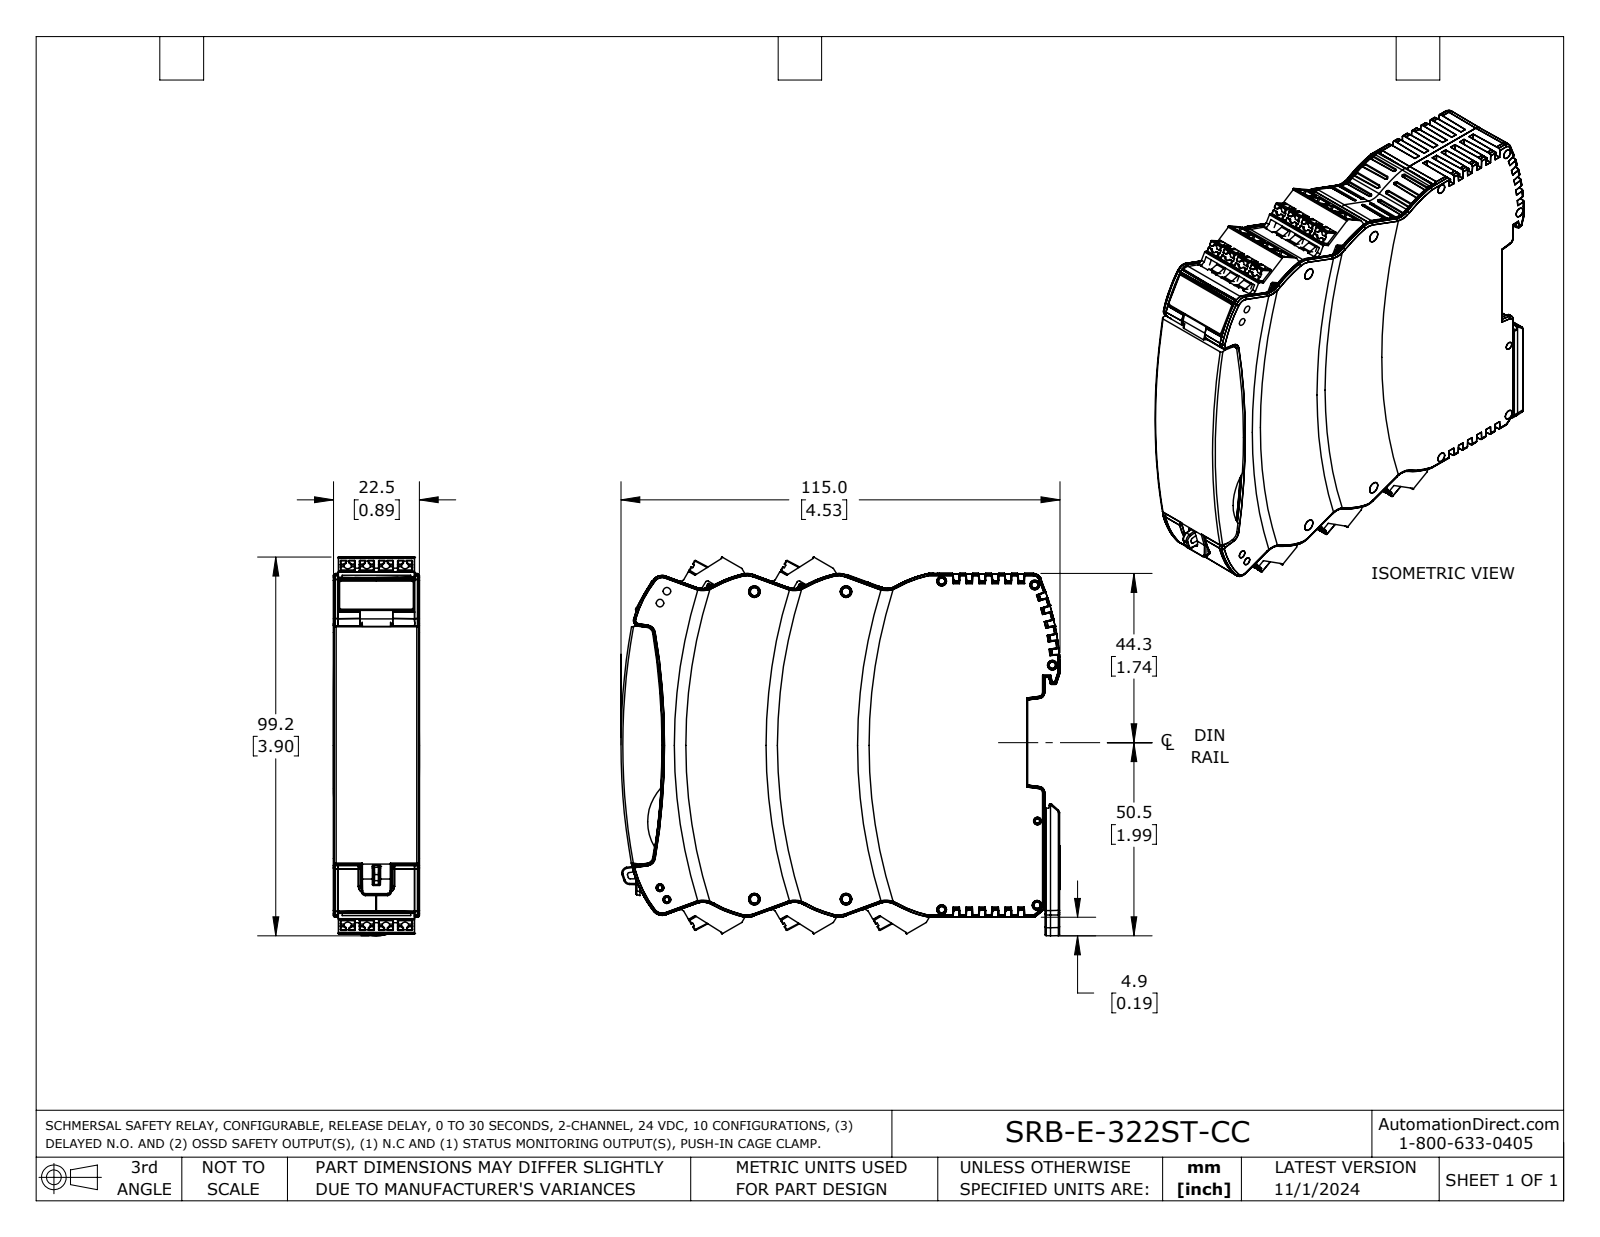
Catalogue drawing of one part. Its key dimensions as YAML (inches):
part_name: "SRB-E-322ST-CC"
step_written_by: "SolidWorks 2023 (AUTOMOTIVE_DESIGN)"
units: inches
bodies: {solids: 2, faces: 4715, planar: 2465, cylindrical: 1391, other: 859}
overall_size: [4.528, 3.904, 0.886]
volume: 12.97
surface_area: 68.52
round_bosses_or_shafts:
  - {diameter: 0.067, count: 1}
partial_cylinders:
  - {radius: 0.008, count: 260}
  - {radius: 0.012, count: 248}
  - {radius: 0.02, count: 206}
  - {radius: 0.01, count: 60}
  - {radius: 0.004, count: 55}
  - {radius: 0.039, count: 34}
  - {radius: 0.059, count: 24}
  - {radius: 0.047, count: 20}
face_to_face_distances: [0.886, 0.133, 0.267, 0.035, 0.177, 0.785, 0.05, 0.05, 0.134, 0.85]
